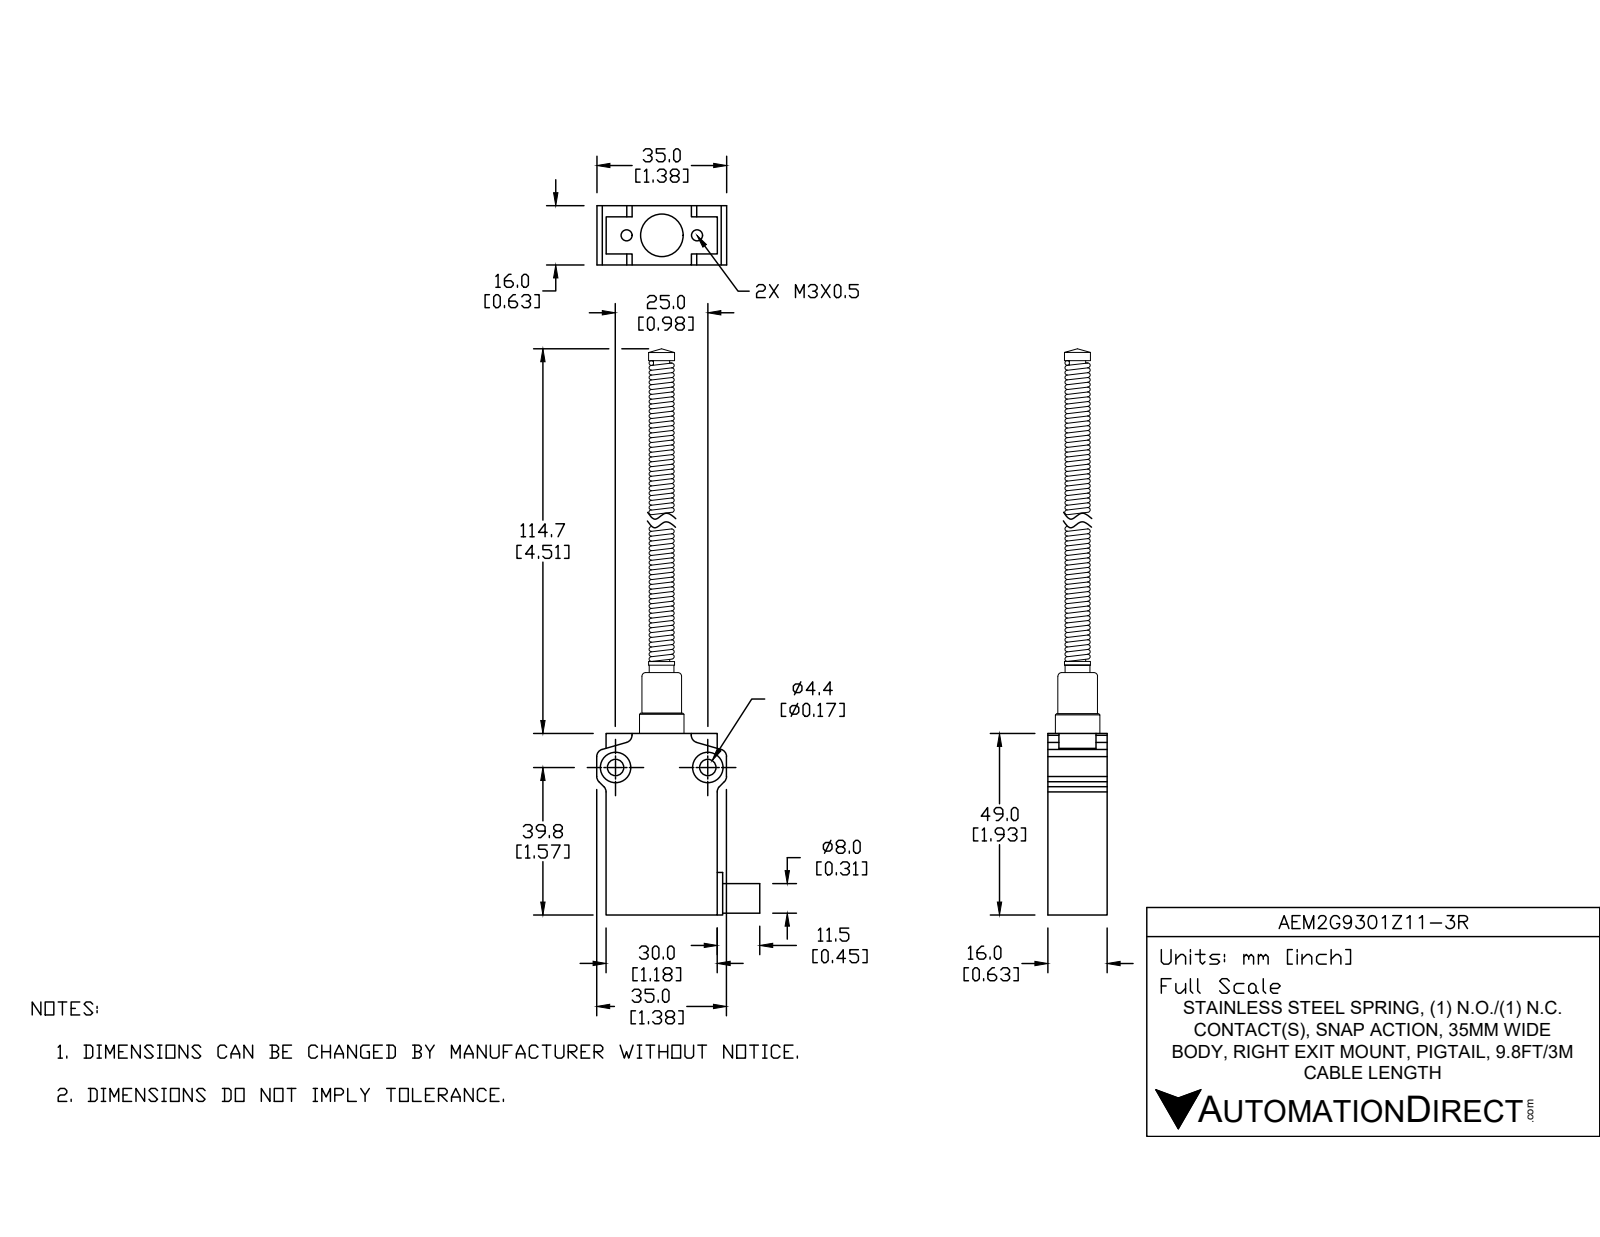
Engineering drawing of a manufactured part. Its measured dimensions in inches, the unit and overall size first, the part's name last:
Units: inches
Overall size (bounding box): 7.031 × 1.378 × 0.63
Round holes (diameter × count): ⌀0.173 ×2, ⌀0.323 ×2
Round bosses / shafts (diameter × count): ⌀0.472 ×1, ⌀0.433 ×1, ⌀0.315 ×1, ⌀0.276 ×1, ⌀0.268 ×1, ⌀0.232 ×1
Partial cylindrical surfaces — rounded edges, fillets, slot ends (radius × count): R0.079 ×8, R0.256 ×1
Main face-to-face distances: 0.63, 1.181, 1.929, 0.472, 1.74, 0.189, 0.098, 1.28, 0.157, 0.512
Hole centre spacings: 0.984
Volume: 1.778 in³ · Surface area: 15.7 in²
Bodies: 3 solids, 129 faces (50 planar, 46 cylindrical, 33 other)
Part name (STEP PRODUCT): AEM2G9301Z11-3R
STEP written by: SolidWorks 2017 (AUTOMOTIVE_DESIGN)
